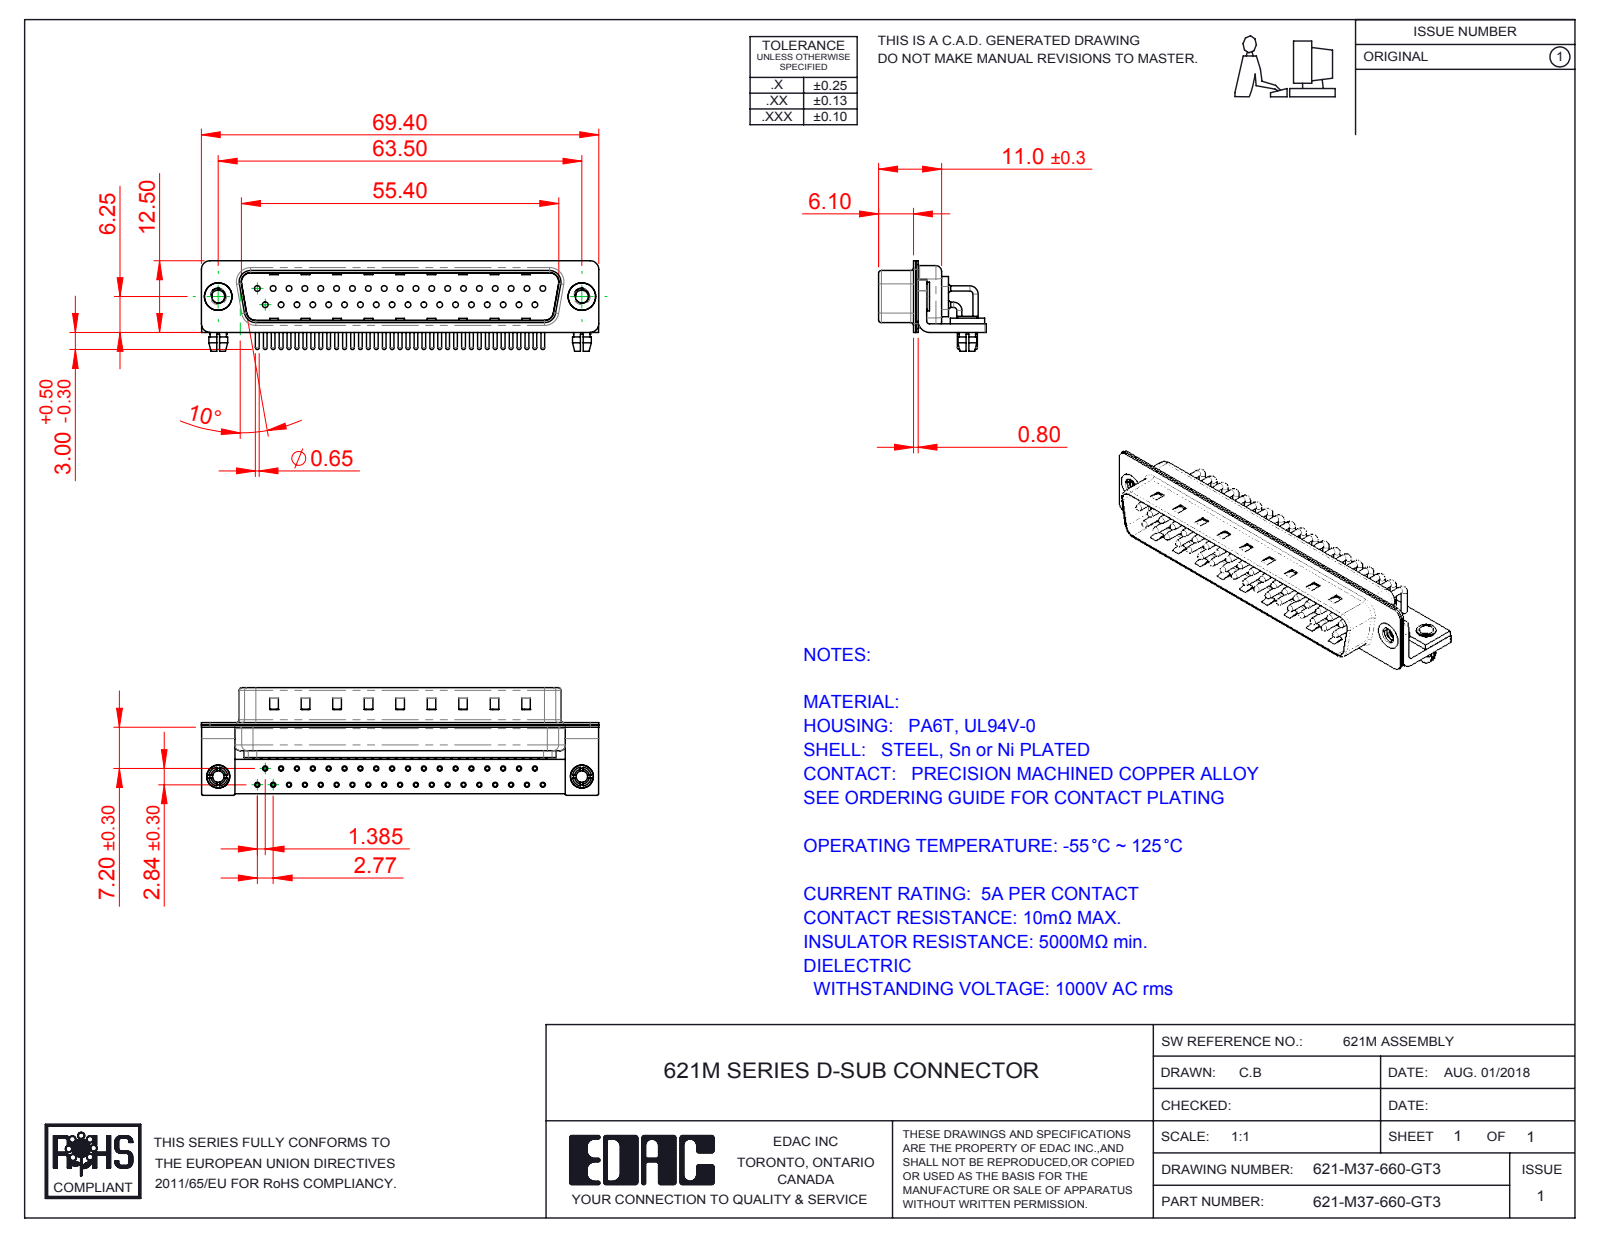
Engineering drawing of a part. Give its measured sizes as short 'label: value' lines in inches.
name: 621M Shell Front_37 Contacts; 621-M37-660-GT3; 621M Board Lock; 621M Shell Rear_37 Contacts (+6 more)
written by: SolidWorks 2016 (CONFIG_CONTROL_DESIGN)
unit: in
bodies: 47 solids, 4698 faces (2645 planar, 1601 cylindrical, 452 other)
size: 2.732 × 0.74 × 0.622
volume: 0.283 in³; area: 18.84 in²
holes: 39× ⌀0.079, 37× ⌀0.035, 37× ⌀0.039, 37× ⌀0.067, 2× ⌀0.089, 2× ⌀0.098, 2× ⌀0.126, 2× ⌀0.157, 2× ⌀0.189
bosses: 46× ⌀0.035, 37× ⌀0.059, 37× ⌀0.026, 2× ⌀0.197, 2× ⌀0.193, 2× ⌀0.157, 2× ⌀0.134, 2× ⌀0.13
rounds: 37× R0.04, 16× R0.01, 16× R0.059, 13× R0.079, 9× R0.02, 8× R0.063, 4× R0.024, 4× R0.026
face distances: 0.016, 0.033, 0.049, 0.376, 0.059, 0.409, 0.327, 0.031, 0.343, 0.039
hole spacings: 0.124, 0.109, 0.218, 0.327, 0.436, 0.545, 0.198, 0.654
